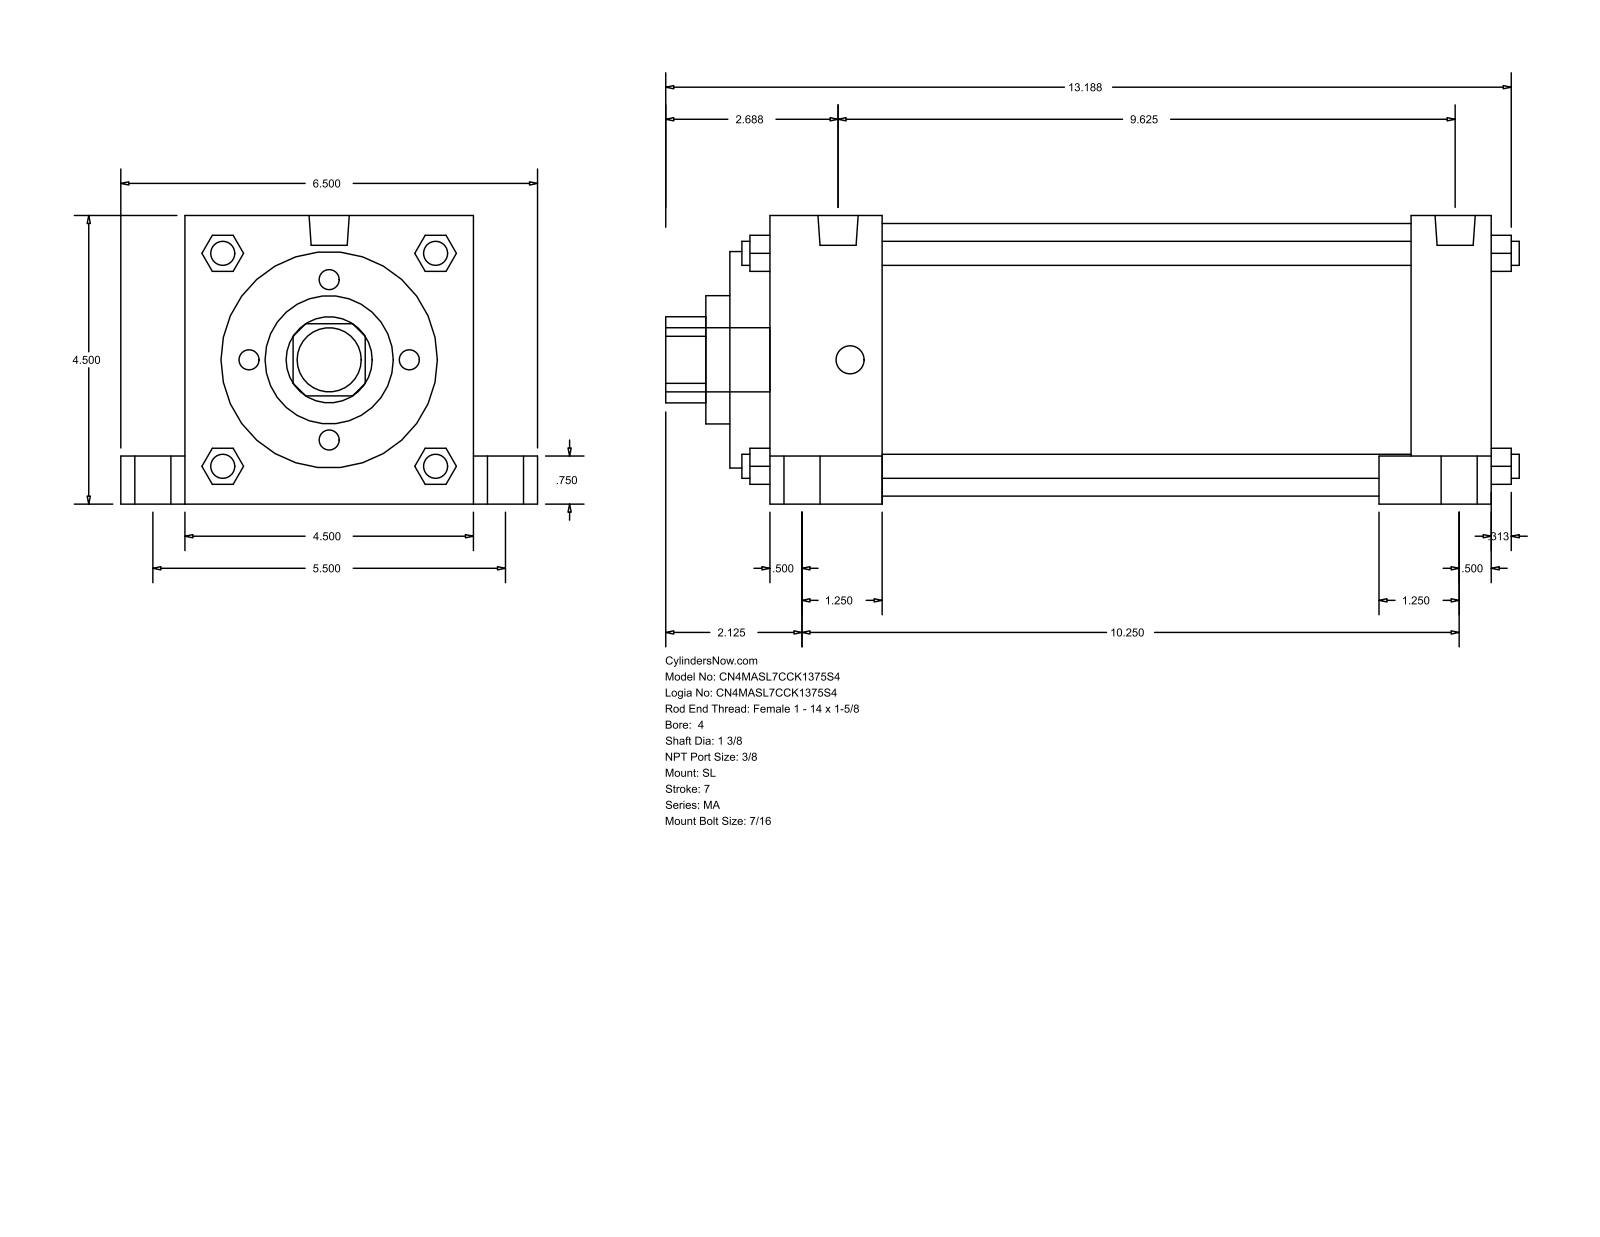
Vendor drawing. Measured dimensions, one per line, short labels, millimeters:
name: MA_SL__0400_1.375
written by: GSSL Pune (CONFIG_CONTROL_DESIGN)
unit: mm
bodies: 0 solids, 150 faces (113 planar, 37 cylindrical, 0 other)
size: 338.14 × 165.1 × 114.3
holes: 1× ⌀34.92, 1× ⌀50.8, 1× ⌀85.72, 1× ⌀107.95
bosses: 4× ⌀20.64, 4× ⌀14.29, 4× ⌀11.11, 4× ⌀9.53, 2× ⌀15.93, 1× ⌀25.4
rounds: 1× R17.06
face distances: 114.3, 285.75, 209.55, 301.62, 15.87, 60.32, 44.45, 241.3, 269.87, 254
